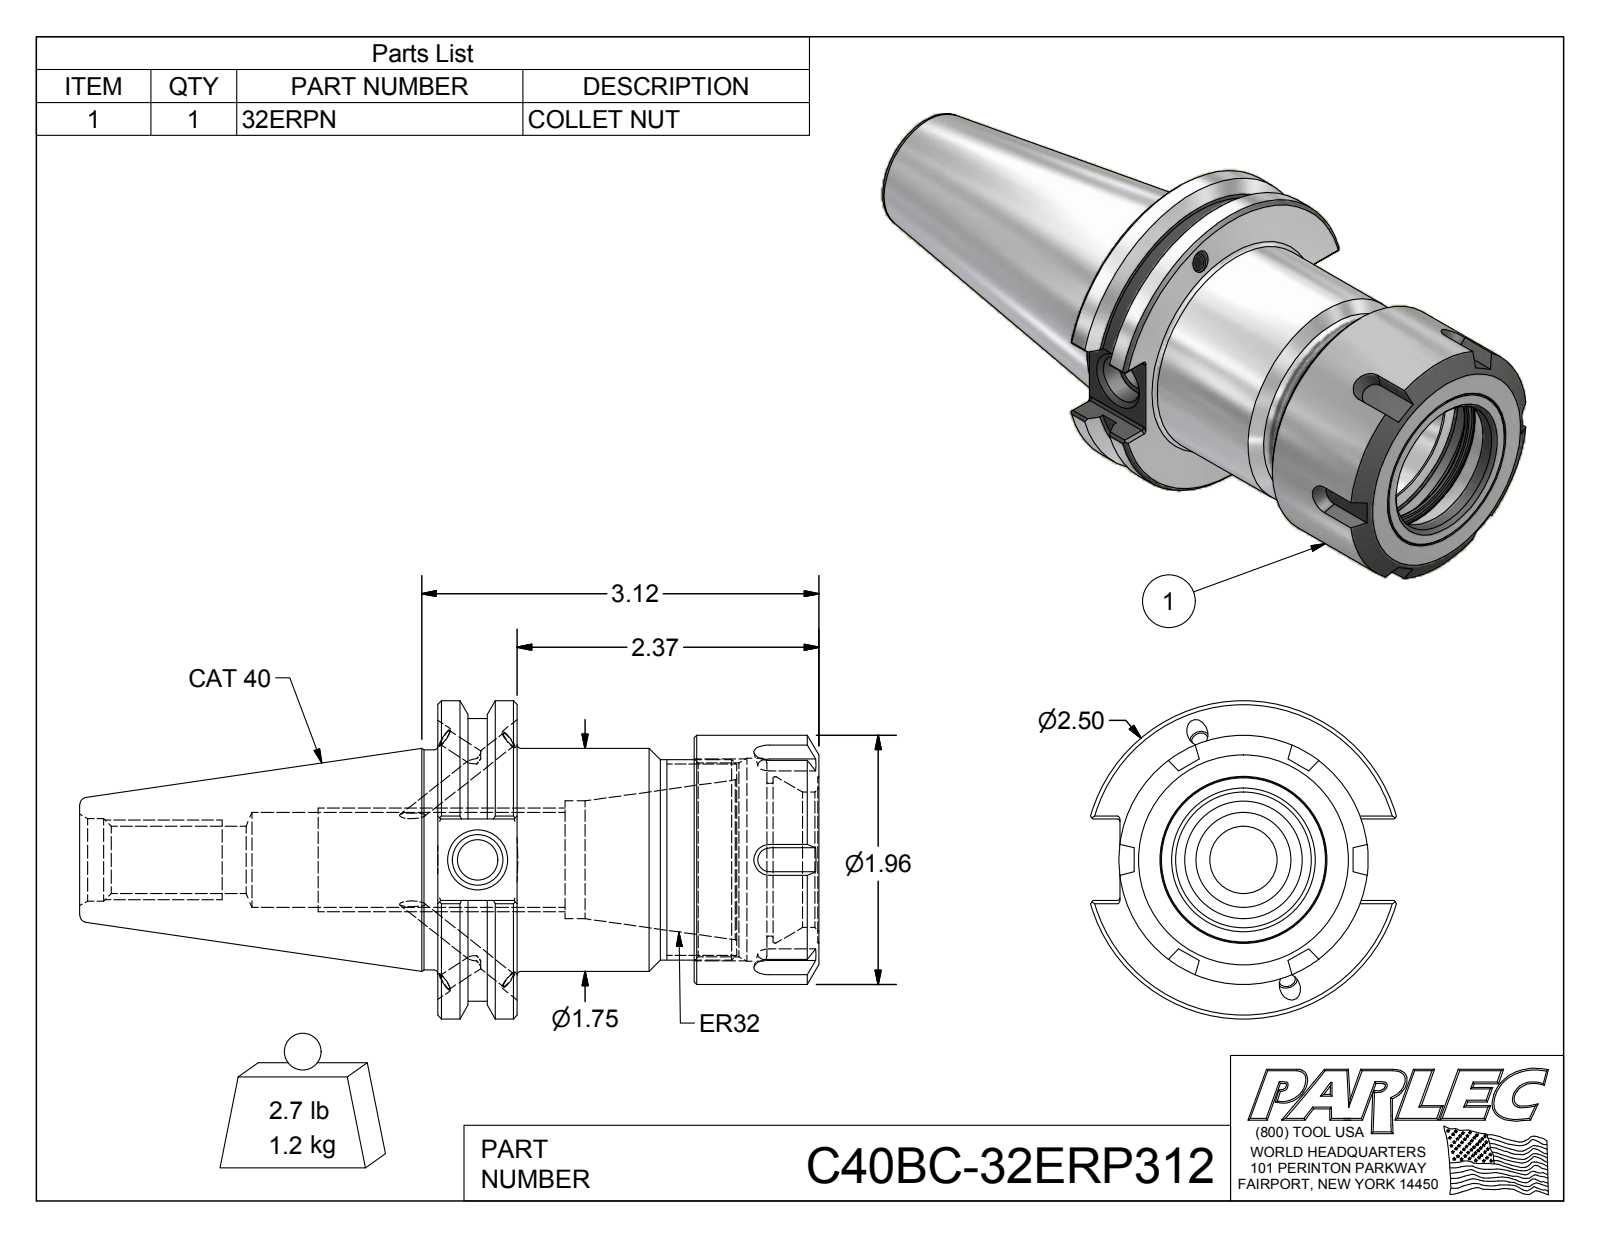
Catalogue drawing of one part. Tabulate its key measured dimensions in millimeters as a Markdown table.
| quantity | value |
| --- | --- |
| part name | C40BC-32ER3-1; 32ERPN; 029-965; C40BC-32ERP312 |
| STEP written by | Autodesk Inventor 2016 (AUTOMOTIVE_DESIGN) |
| units | millimeters |
| bodies | 6 solids, 209 faces (99 planar, 53 cylindrical, 57 other) |
| overall size | 147.51 × 63.5 × 61.05 |
| volume | 154 565 mm³ |
| surface area | 40 302 mm² |
| round holes (diameter × count) | 3.3 × 4, 4.1 × 4, 8 × 1, 10.13 × 1, 13.39 × 1, 16.46 × 1, 18.92 × 1, 23.5 × 1, 27 × 1, 30.48 × 1, 33.15 × 1, 38.68 × 1 |
| round bosses / shafts (diameter × count) | 4.2 × 4, 4 × 4, 63.5 × 1, 56.36 × 1, 49.73 × 1, 44.45 × 1, 43.94 × 1, 40 × 1 |
| partial cylindrical surfaces (radius × count) | 0.51 × 12 |
| main face-to-face distances | 15.88, 76.08, 60.2, 51.23, 35.35, 24.85, 65.74, 49.86, 14.51, 10.34 |
